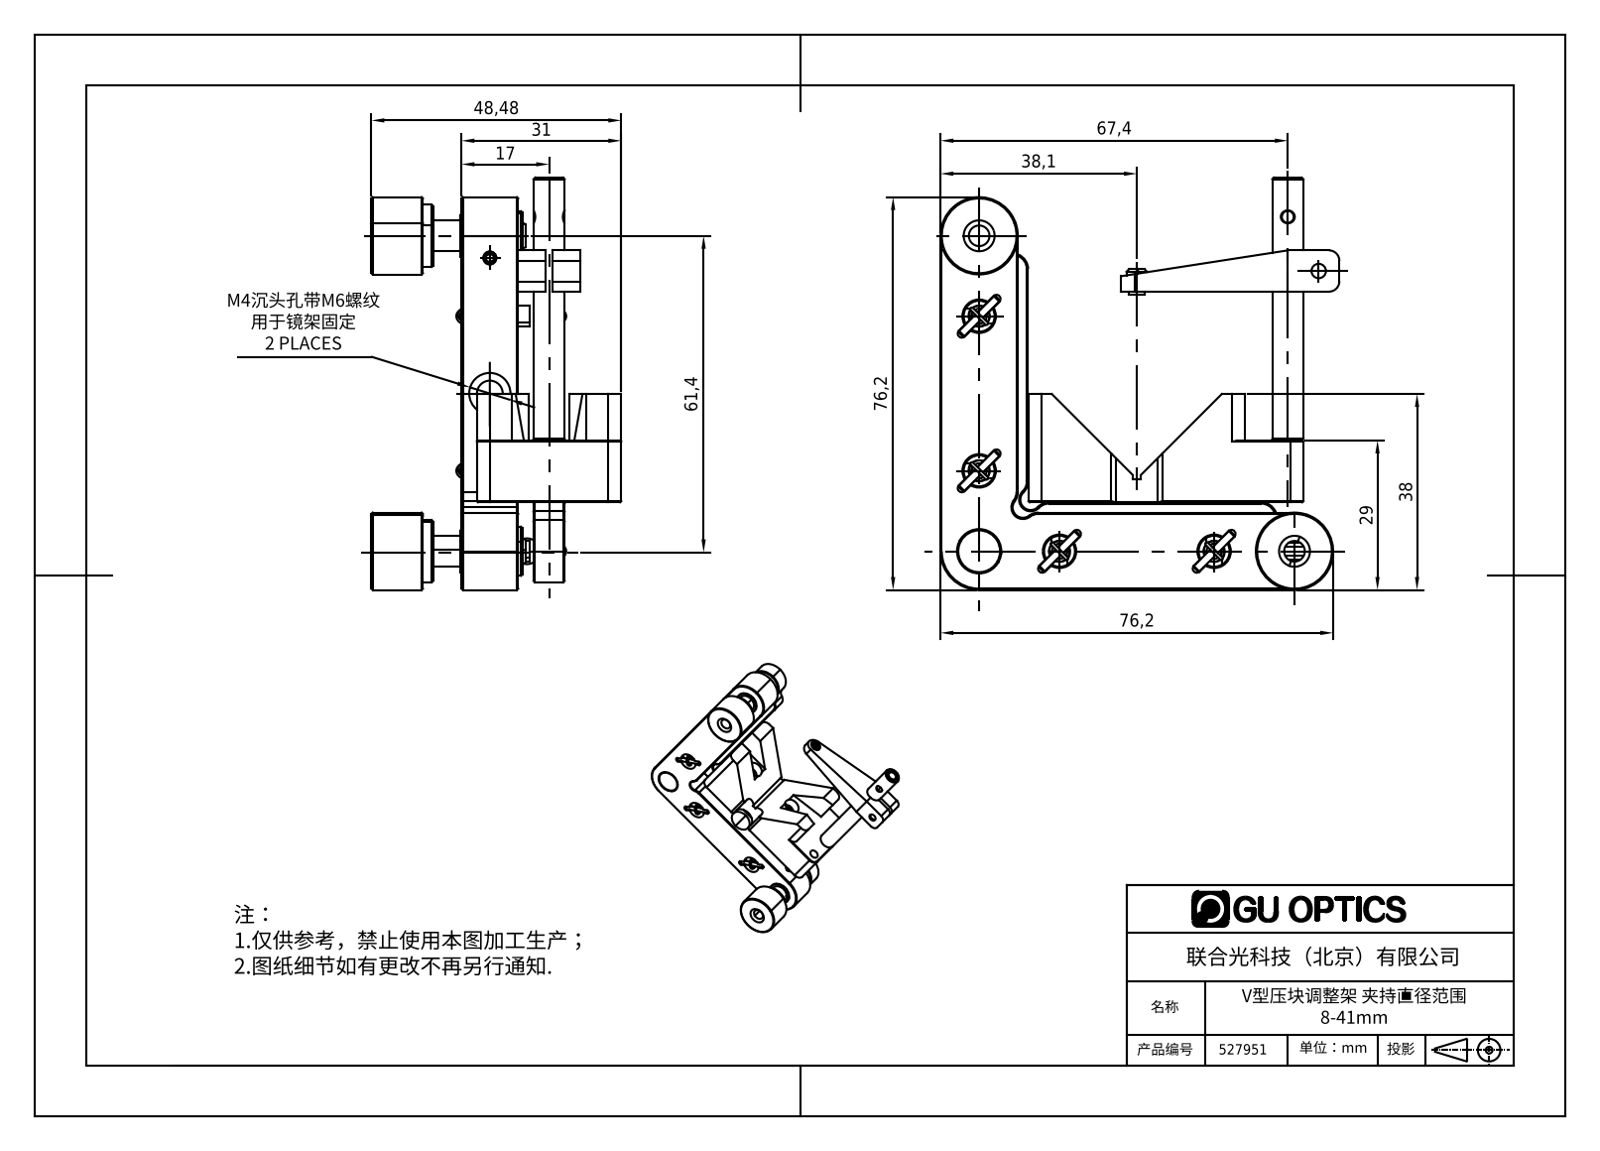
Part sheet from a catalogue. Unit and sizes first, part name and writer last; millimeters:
Units: millimetres
Overall size (bounding box): 80 × 77.4 × 48.48
Round holes (diameter × count): ⌀6 ×7, ⌀3.3 ×4, ⌀6.5 ×4, ⌀8.6 ×3, ⌀2.5 ×2, ⌀3 ×2, ⌀4 ×2, ⌀5 ×2, ⌀8 ×2, ⌀2.3 ×1, ⌀2.8 ×1
Round bosses / shafts (diameter × count): ⌀1.5 ×6, ⌀4 ×5, ⌀3 ×5, ⌀9.5 ×3, ⌀6 ×3, ⌀15 ×2, ⌀12 ×2
Partial cylindrical surfaces — rounded edges, fillets, slot ends (radius × count): R0.8 ×8, R3 ×7, R2.5 ×6, R2 ×4, R1 ×2, R6 ×1, R7.5 ×1
Main face-to-face distances: 11, 20, 3, 14, 17, 9, 6, 15, 2, 1.5
Hole centre spacings: 15.6, 45.6, 15.31, 10, 10.1, 11.88, 21.65, 30
Bodies: 0 solids, 485 faces (181 planar, 154 cylindrical, 150 other)
Part name (STEP PRODUCT): 527951
STEP written by: SolidWorks 2020 (CONFIG_CONTROL_DESIGN)
